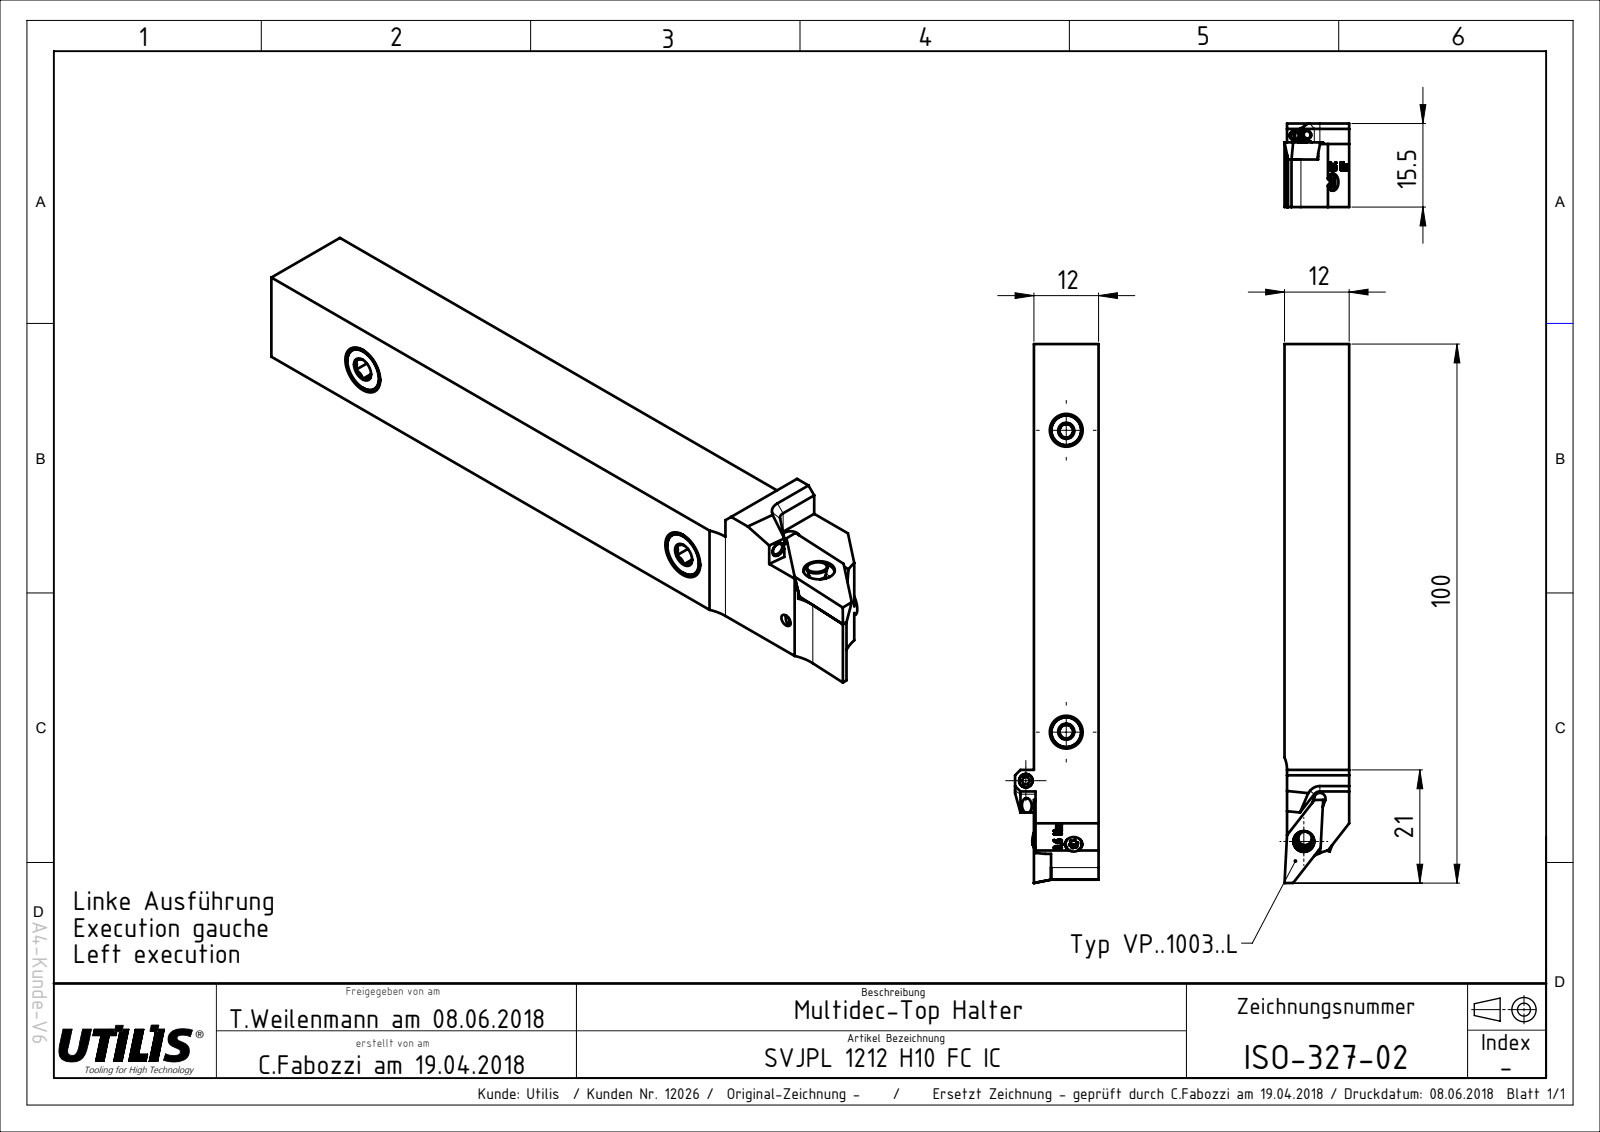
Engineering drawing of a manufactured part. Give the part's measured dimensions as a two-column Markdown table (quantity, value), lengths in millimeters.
| quantity | value |
| --- | --- |
| part name | ISO-327-02 |
| STEP written by | SolidWorks 2017 (AUTOMOTIVE_DESIGN) |
| units | millimeters |
| bodies | 1 solid, 124 faces (63 planar, 8 cylindrical, 53 other) |
| overall size | 100 × 15.5 × 12 |
| volume | 13 672 mm³ |
| surface area | 5 054 mm² |
| round holes (diameter × count) | 3.2 × 1 |
| partial cylindrical surfaces (radius × count) | 1.05 × 1, 1.31 × 1, 6 × 1, 6.1 × 1, 8.81 × 1 |
| main face-to-face distances | 12, 0.47, 11.53, 11.7, 79, 15.5, 3.8, 3.5, 2, 4 |
